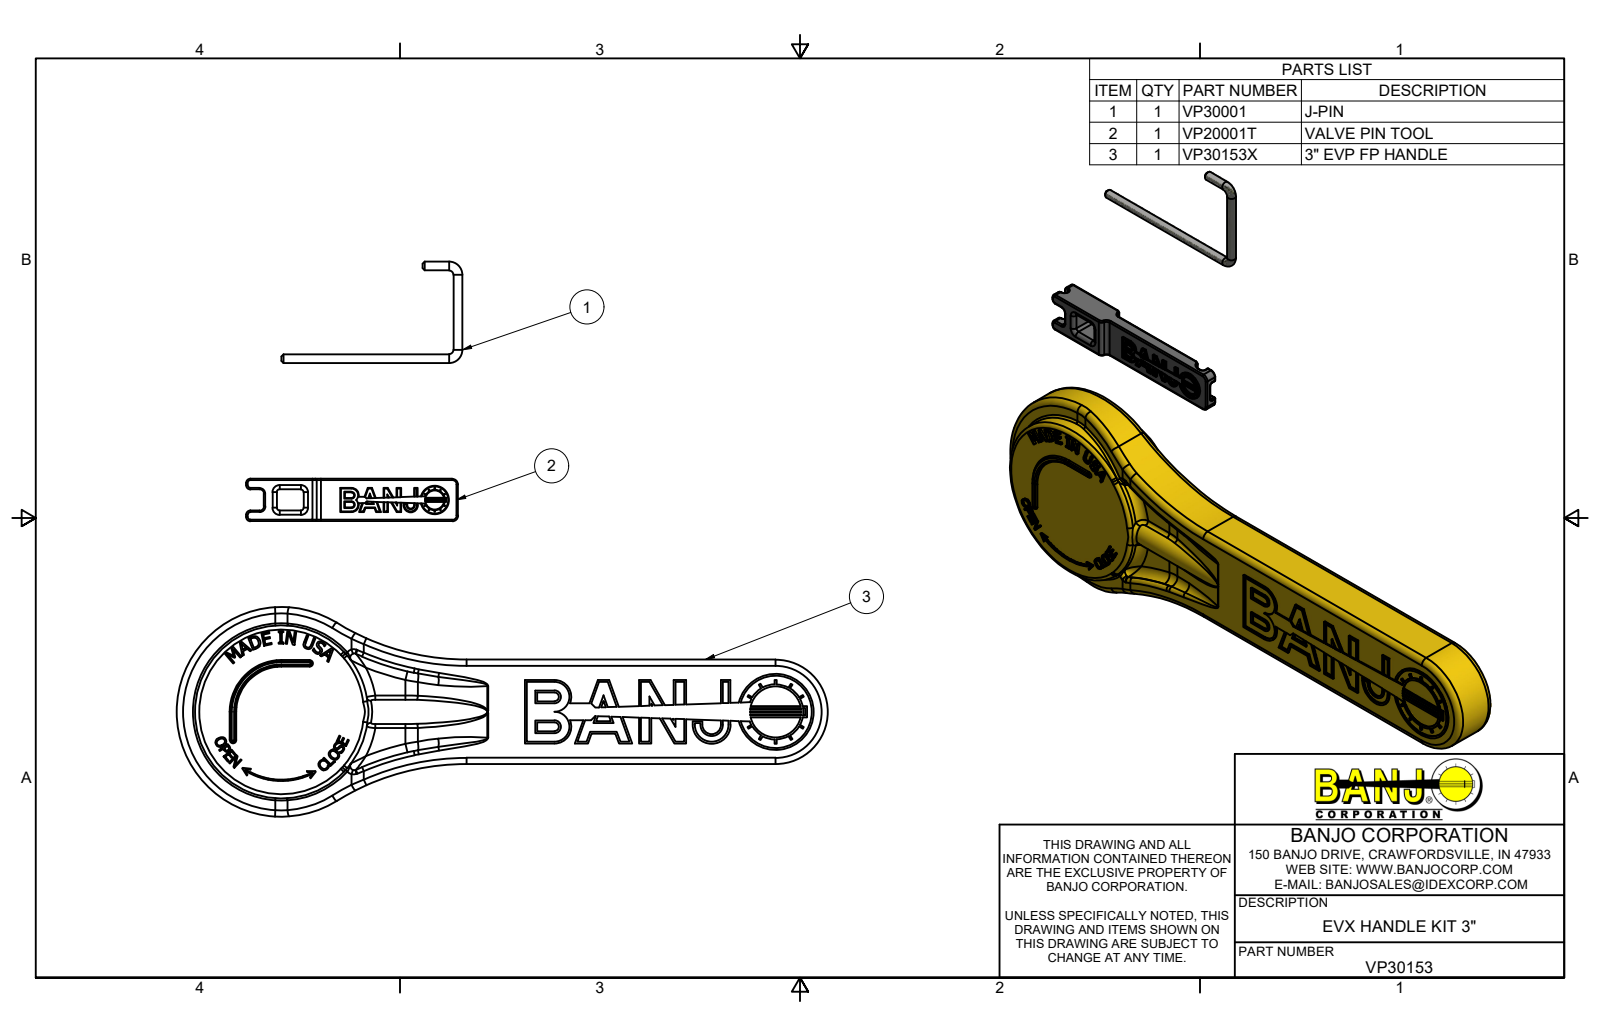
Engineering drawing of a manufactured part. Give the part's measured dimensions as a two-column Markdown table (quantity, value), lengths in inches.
| quantity | value |
| --- | --- |
| part name | VP30153; VP30153X; VP20001T; VP30001 |
| STEP written by | Autodesk Inventor 2021 (AUTOMOTIVE_DESIGN) |
| units | inches |
| bodies | 3 solids, 1393 faces (748 planar, 242 cylindrical, 403 other) |
| overall size | 9.224 × 7.859 × 1.28 |
| volume | 10.2 in³ |
| surface area | 63.86 in² |
| round holes (diameter × count) | 0.272 × 1, 0.385 × 1, 0.726 × 1, 1.026 × 1 |
| round bosses / shafts (diameter × count) | 0.125 × 3, 2.969 × 1, 2.449 × 1, 1.08 × 1, 0.405 × 1 |
| partial cylindrical surfaces (radius × count) | 0.02 × 28, 0.06 × 28, 0.01 × 10, 0.015 × 8, 0.09 × 8, 0.04 × 4, 0.05 × 4, 0.062 × 4 |
| main face-to-face distances | 0.69, 0.06, 0.75, 0.3, 0.39, 0.36, 0.5, 1.48, 0.26, 1.22 |
| hole center spacings | 5.686 |
